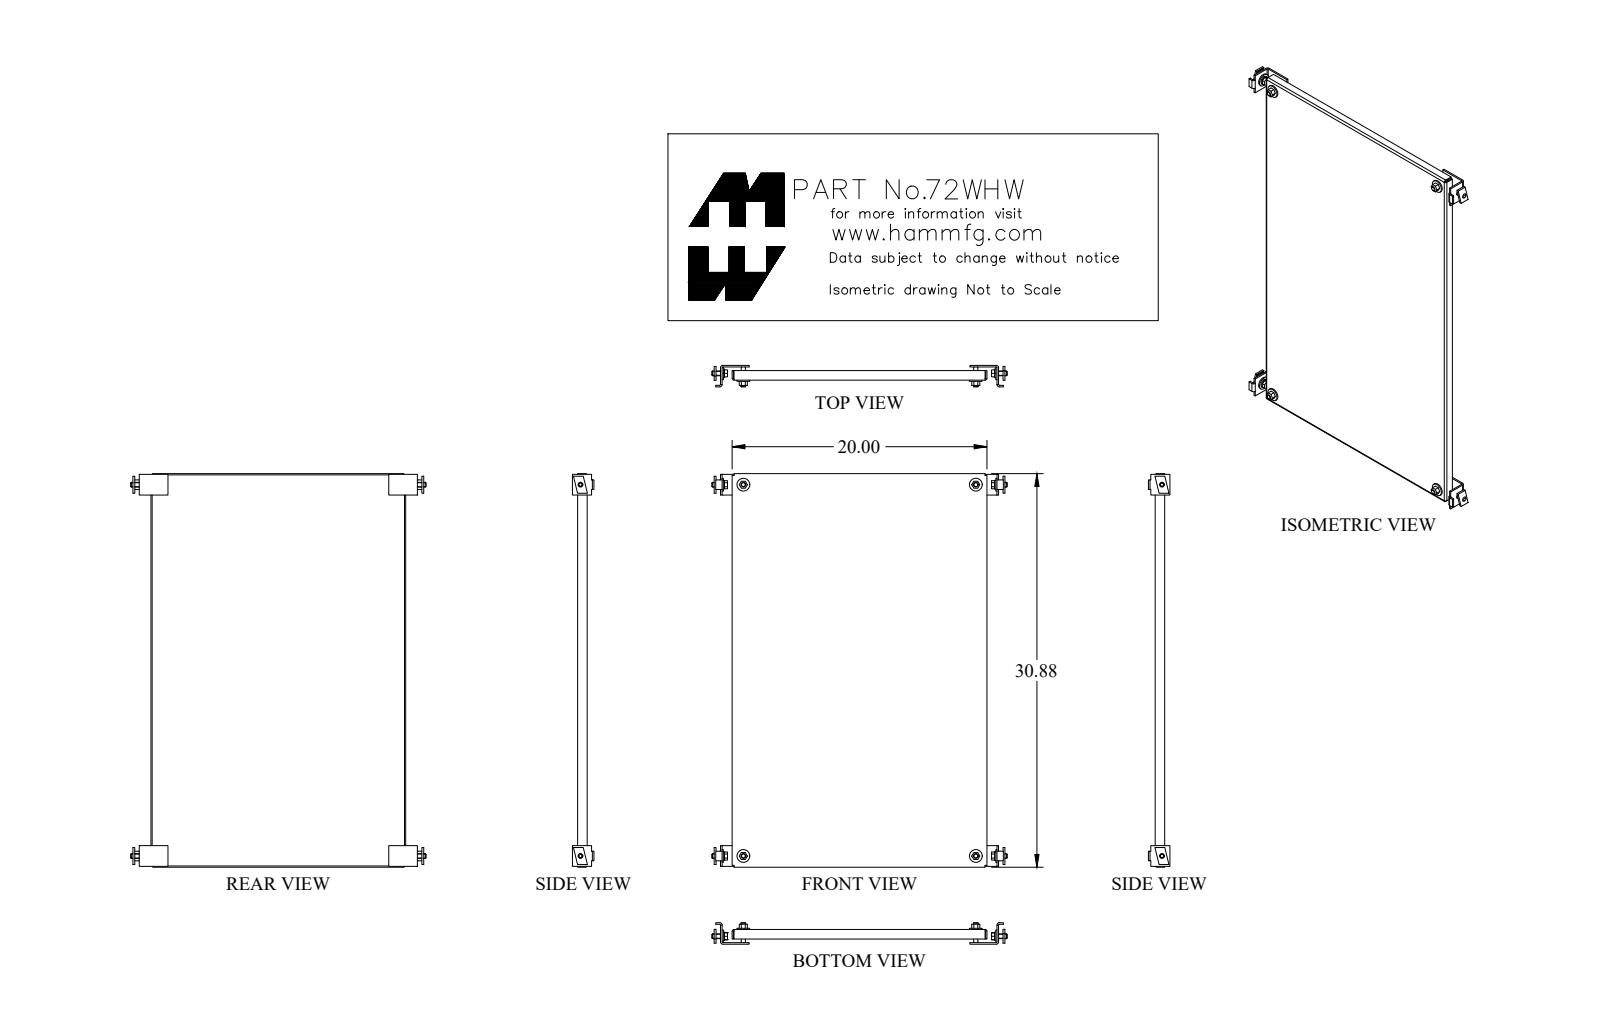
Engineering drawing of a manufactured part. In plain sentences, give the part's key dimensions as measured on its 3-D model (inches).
The part is named "72WHW_Default". Its 3-D file was written by "SolidWorks 2018 (CONFIG_CONTROL_DESIGN)". It is 1 solid with 38 faces: 22 planar, 16 cylindrical and 0 other. Overall it measures 30.875 by 20 by 0.75 inches. Its volume is 64.43 cubic inches and its surface area 1 367 square inches. Round holes: 4 of diameter 0.563. Partial cylindrical surfaces (rounded edges, fillets, slot ends): 4 of radius 0.048, 4 of radius 0.143. The main face-to-face distances are 0.095, 19.905, 30.78, 19.81, 20, 30.875, 30.685, 0.75, 0.655, 0.143. The hole center spacings are 18.25, 29.125, 34.37.
